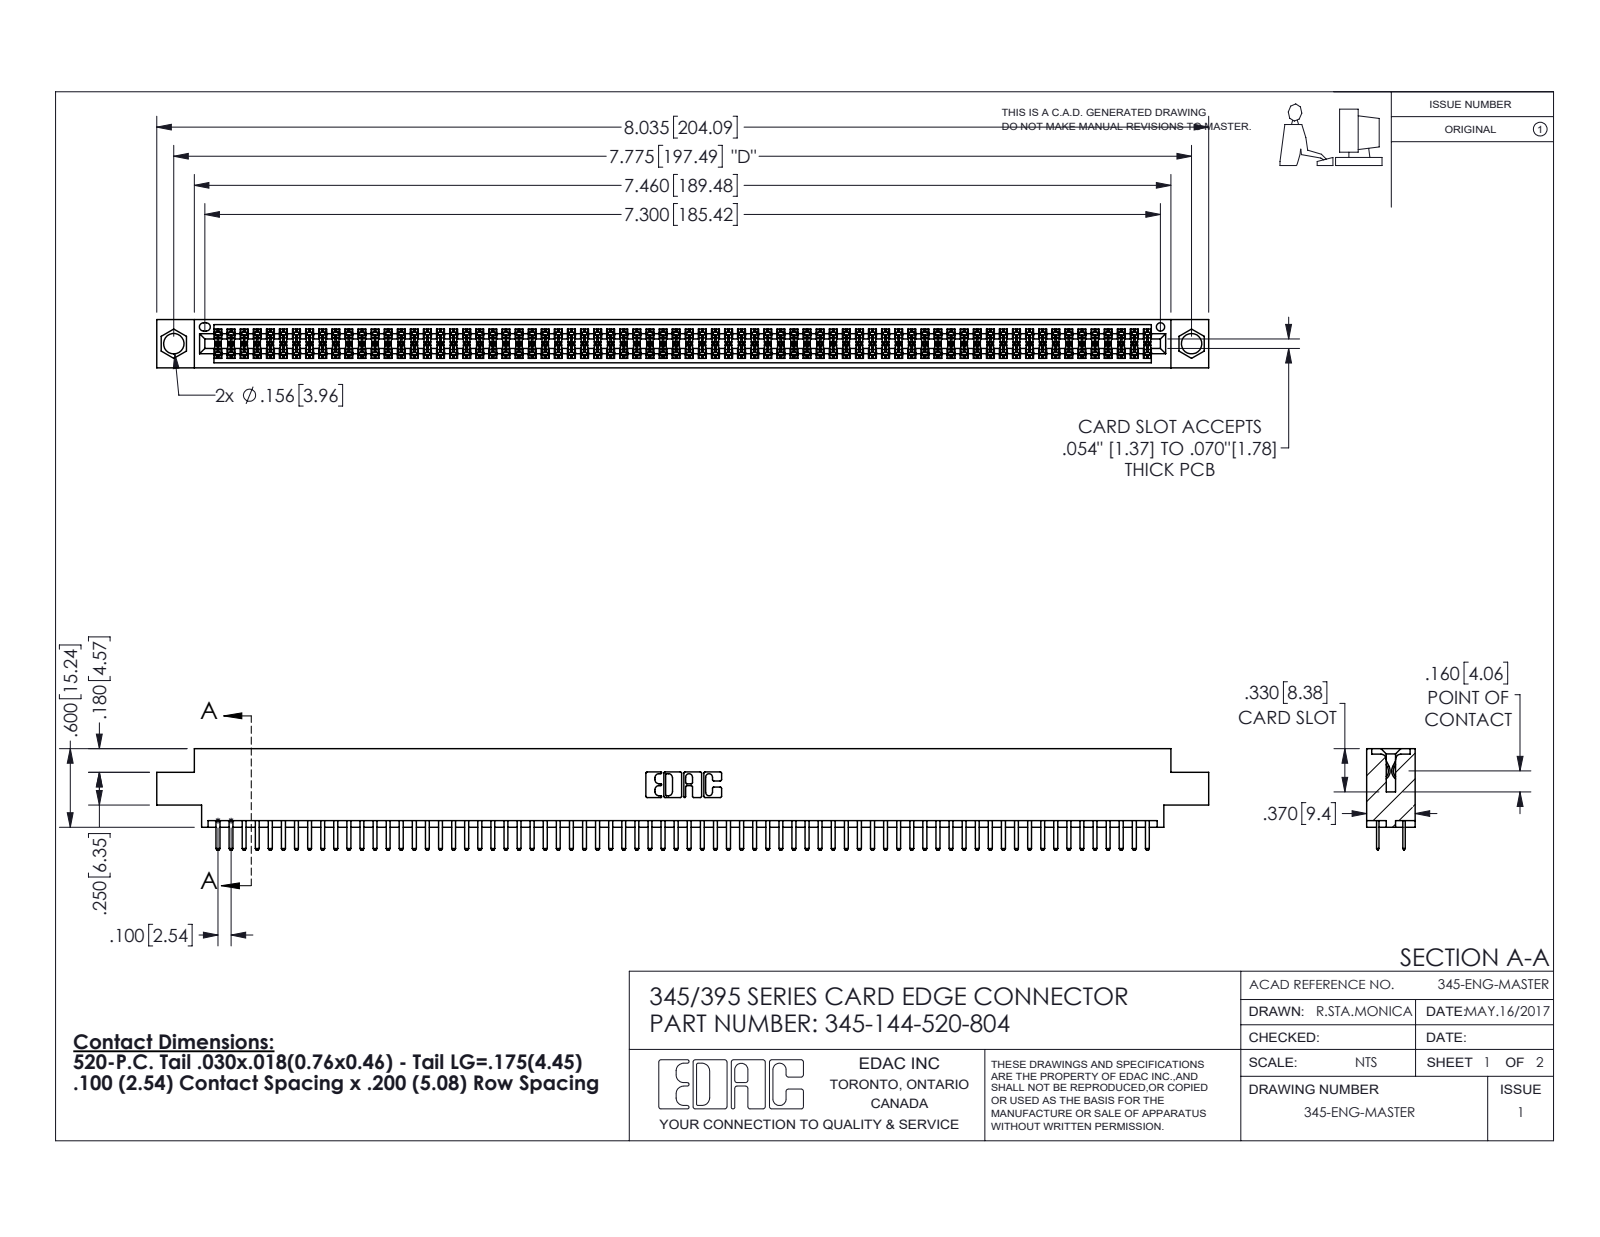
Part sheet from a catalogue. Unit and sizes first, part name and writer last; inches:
Units: inches
Overall size (bounding box): 8.035 × 0.775 × 0.37
Round holes (diameter × count): ⌀0.156 ×2, ⌀0.064 ×1
Partial cylindrical surfaces — rounded edges, fillets, slot ends (radius × count): R0.006 ×216, R0.01 ×148, R0.01 ×22, R0.007 ×6, R0.031 ×6, R0.026 ×3, R0.014 ×2, R0.019 ×2
Main face-to-face distances: 0.072, 0.298, 0.2, 0.37, 0.098, 0.272, 0.025, 0.225, 0.022, 0.072
Hole centre spacings: 0.27, 7.539, 7.775
Volume: 1.21 in³ · Surface area: 46.1 in²
Bodies: 145 solids, 7920 faces (5138 planar, 2782 cylindrical, 0 other)
Part name (STEP PRODUCT): 345-144-520-804; 345 Part_0.170 Offset - 0.156 Dia-TI; 345-292-001_345-293-120
STEP written by: SolidWorks 2020 (CONFIG_CONTROL_DESIGN)
